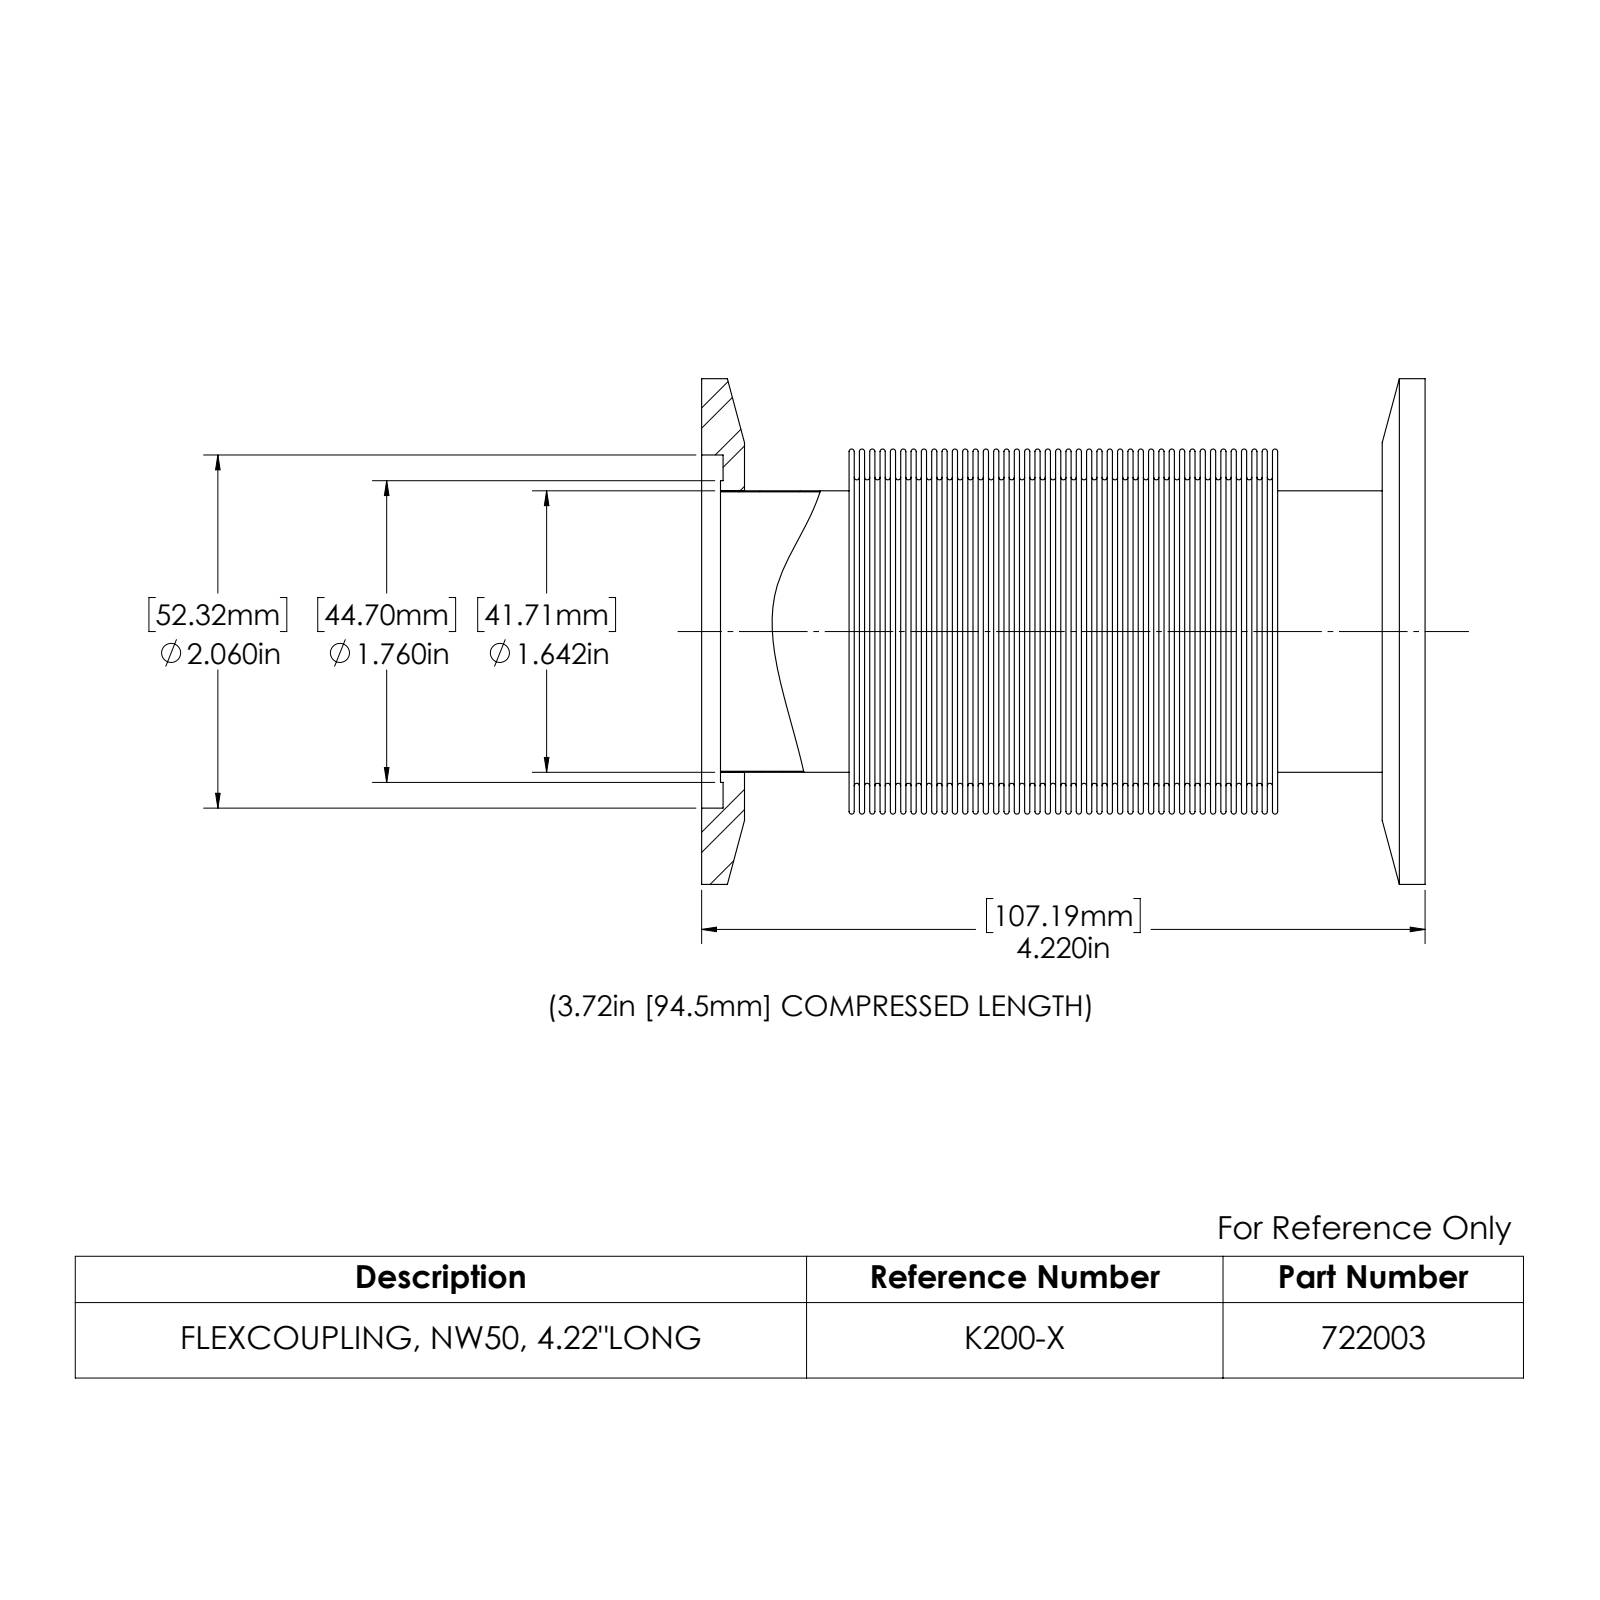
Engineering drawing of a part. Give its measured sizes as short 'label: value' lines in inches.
name: 722003_B
written by: SolidWorks 2022 (CONFIG_CONTROL_DESIGN)
unit: in
bodies: 3 solids, 702 faces (178 planar, 24 cylindrical, 500 other)
size: 4.22 × 2.95 × 2.95
volume: 2.404 in³; area: 243.9 in²
holes: 1× ⌀1.63, 1× ⌀1.642, 1× ⌀2.06
bosses: 1× ⌀2.95, 1× ⌀1.76
face distances: 0.06, 0.12, 0.181, 0.241, 0.301, 0.361, 0.422, 0.482, 0.542, 4.22
